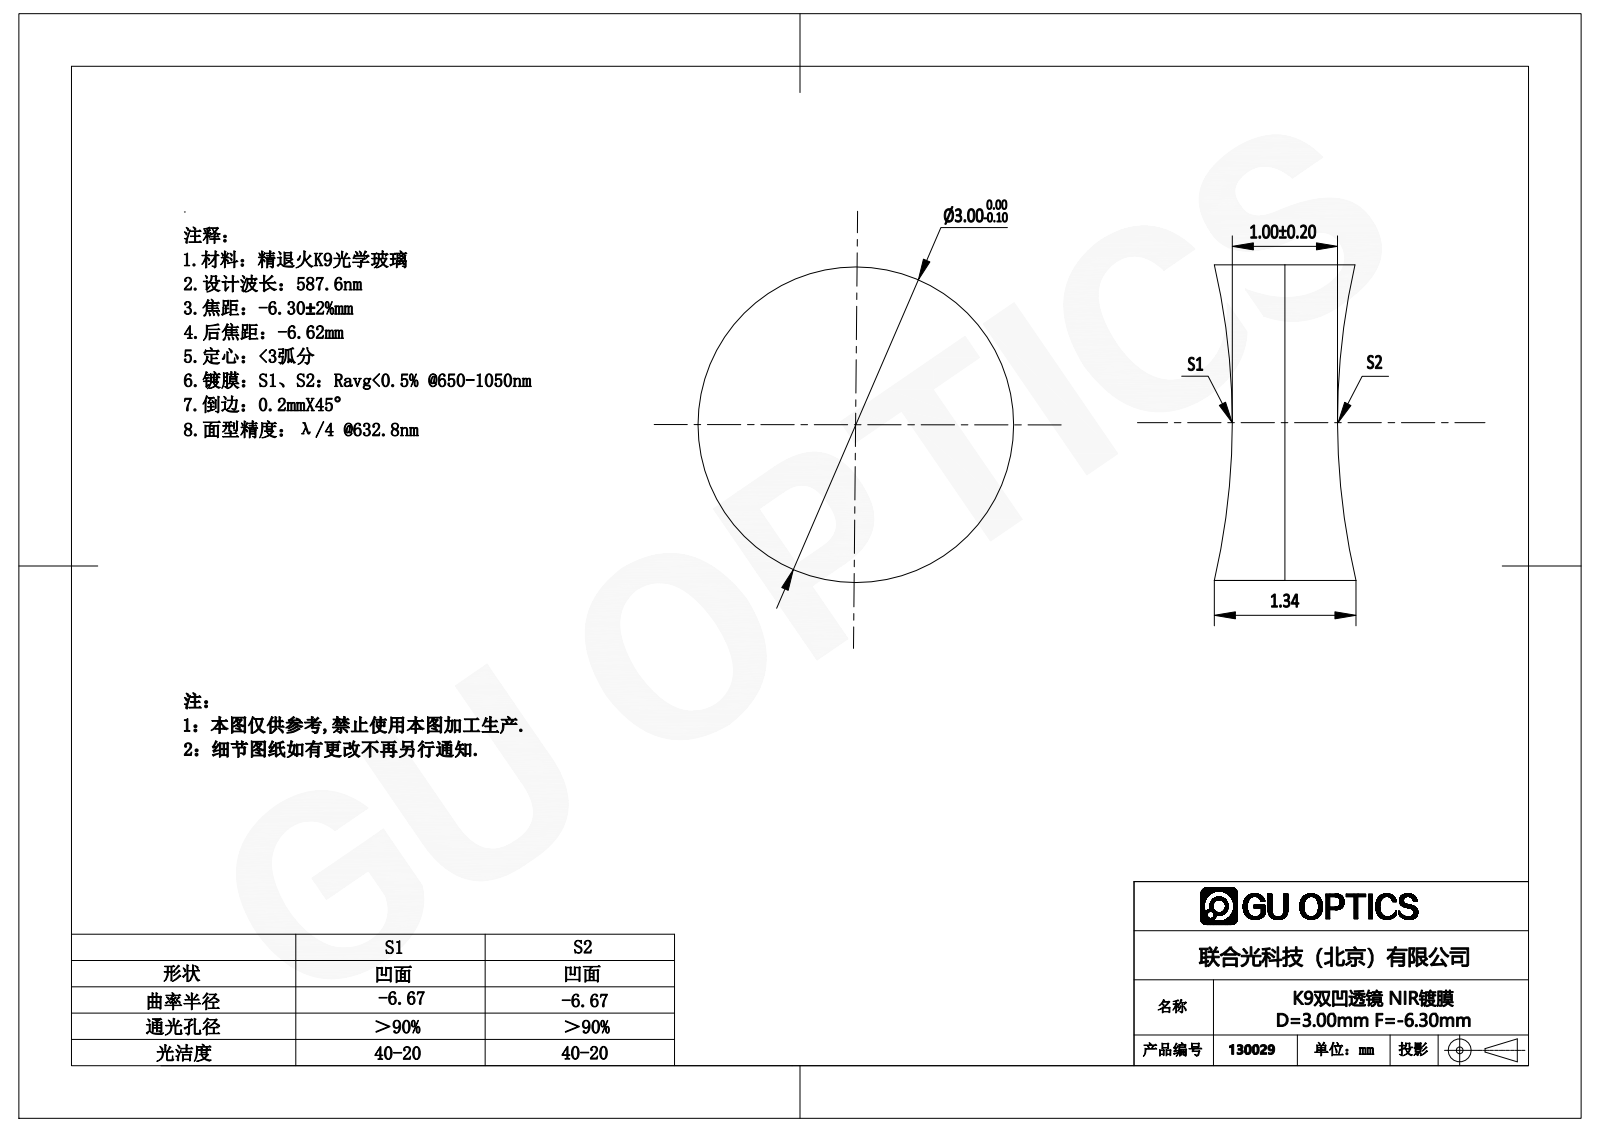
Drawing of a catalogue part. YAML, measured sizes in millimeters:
part_name: "130003"
step_written_by: "SolidWorks 2016 (AUTOMOTIVE_DESIGN)"
units: millimeters
bodies: {solids: 1, faces: 6, planar: 0, cylindrical: 2, other: 4}
overall_size: [3, 3, 1.34]
volume: 8
surface_area: 27
round_bosses_or_shafts:
  - {diameter: 3, count: 1}
